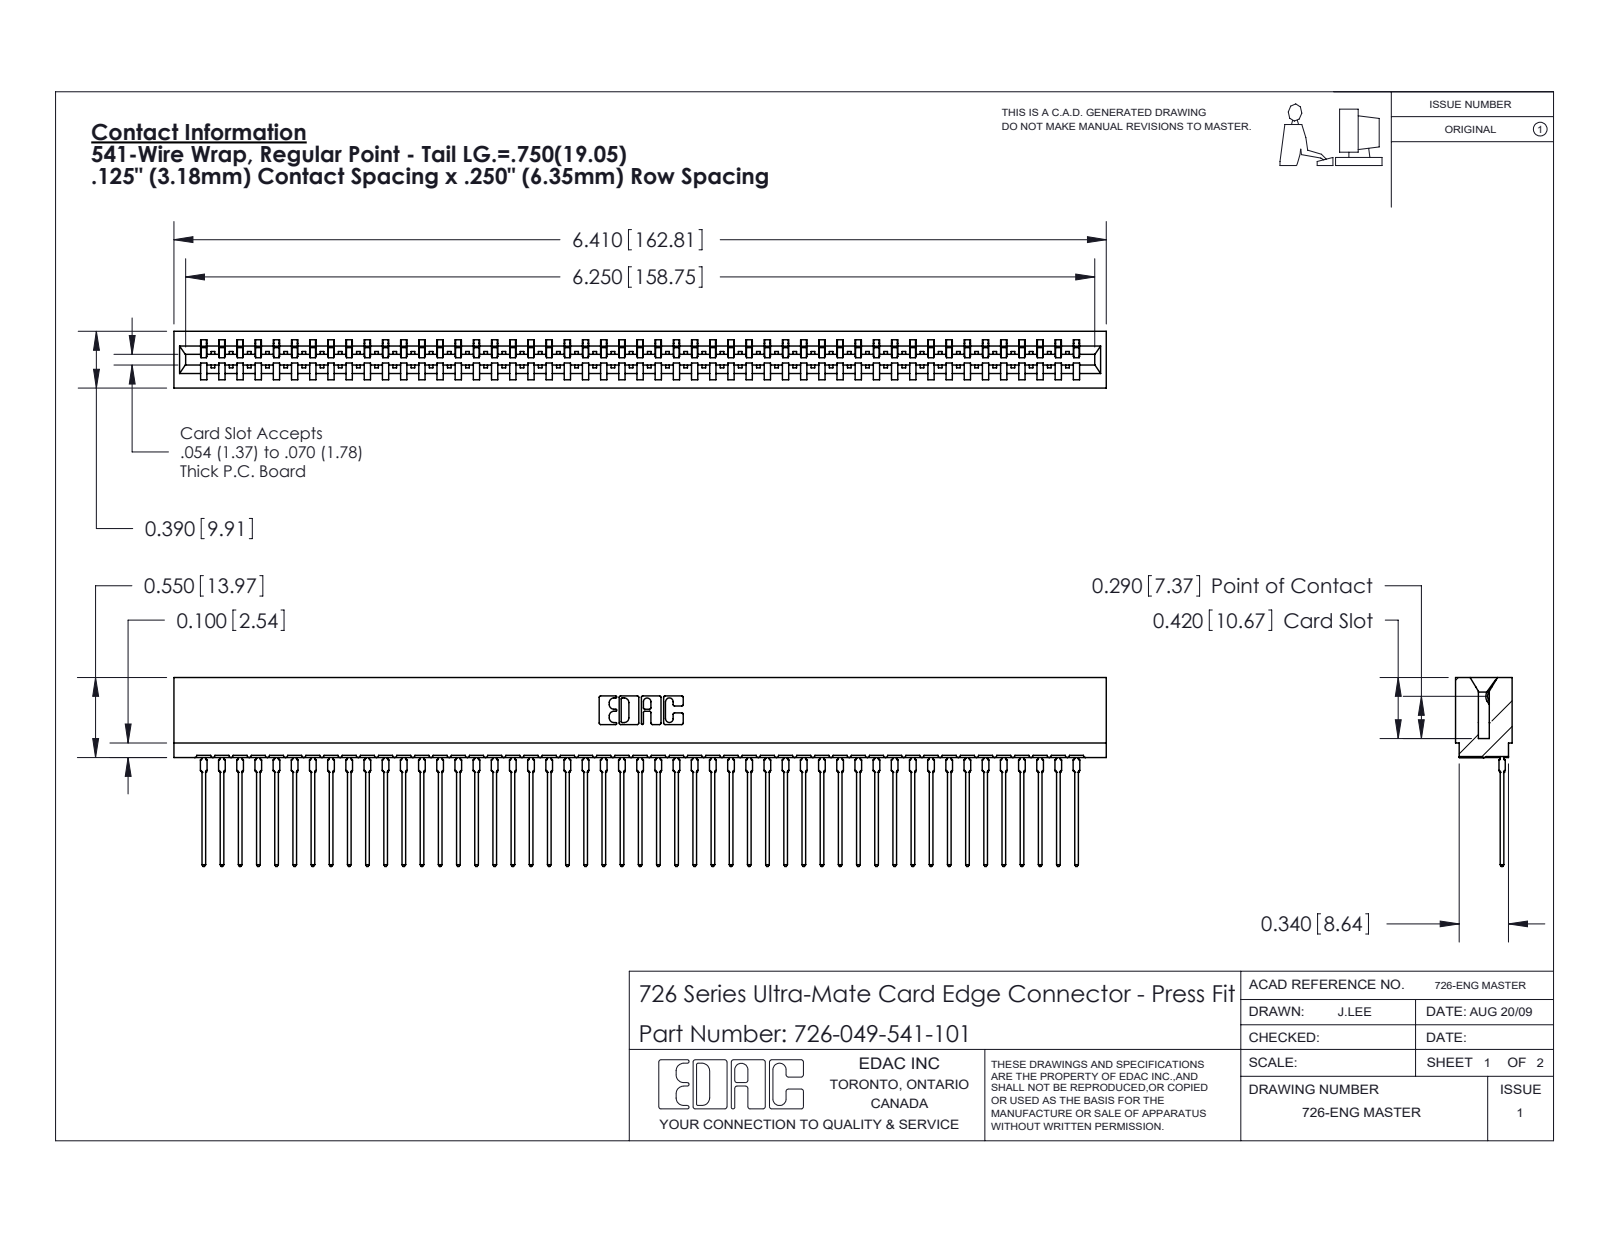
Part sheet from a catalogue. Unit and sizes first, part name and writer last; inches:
Units: inches
Overall size (bounding box): 6.41 × 1.299 × 0.39
Partial cylindrical surfaces — rounded edges, fillets, slot ends (radius × count): R0.021 ×98, R0.015 ×50, R0.01 ×22, R0.007 ×6, R0.031 ×6, R0.005 ×4, R0.011 ×4, R0.026 ×3
Main face-to-face distances: 0.057, 0.333, 0.39, 0.025, 0.307, 0.25, 0.083, 0.275, 0.365, 0.032
Volume: 0.899 in³ · Surface area: 36.82 in²
Bodies: 50 solids, 5389 faces (3142 planar, 973 cylindrical, 1274 other)
Part name (STEP PRODUCT): 746-292-001_541; 726 Part_.515 Slot Depth - 01; 726-049-541-101
STEP written by: SolidWorks 2020 (CONFIG_CONTROL_DESIGN)
